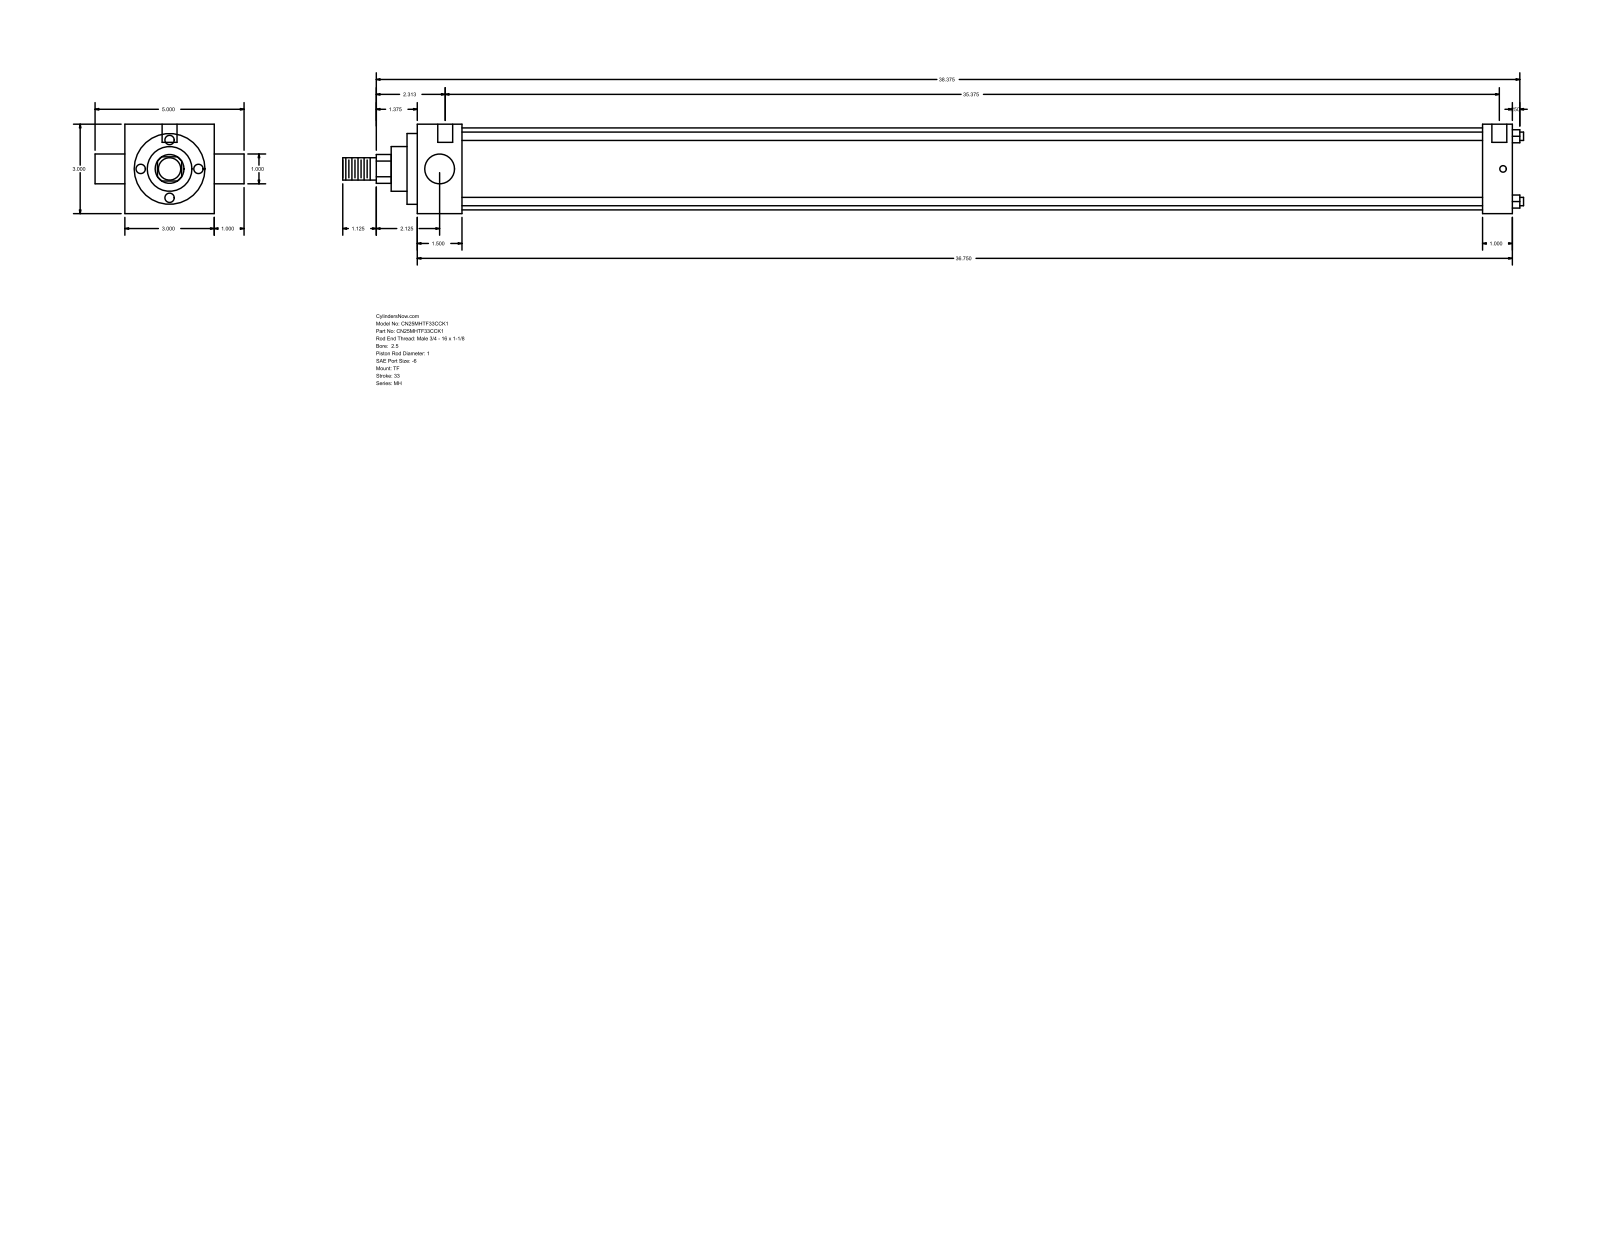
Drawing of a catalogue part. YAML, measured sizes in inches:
part_name: "MH_TF__0250_1"
step_written_by: "GSSL Pune (CONFIG_CONTROL_DESIGN)"
units: inches
bodies: {solids: 0, faces: 86, planar: 61, cylindrical: 25, other: 0}
overall_size: [39.625, 5, 3]
round_holes:
  - {diameter: 0.219, count: 3}
  - {diameter: 0.5, count: 2}
round_bosses_or_shafts:
  - {diameter: 0.281, count: 4}
  - {diameter: 1, count: 2}
  - {diameter: 2.75, count: 1}
  - {diameter: 2.375, count: 1}
  - {diameter: 1.5, count: 1}
  - {diameter: 0.75, count: 1}
partial_cylinders:
  - {radius: 0.484, count: 1}
face_to_face_distances: [3, 36.75, 1, 1.5, 35.25, 35.75, 34.25, 0.344, 1.844, 36.094]
hole_center_spacings: [0.125, 0.187, 35.375, 35.5, 35.562, 35.687]
